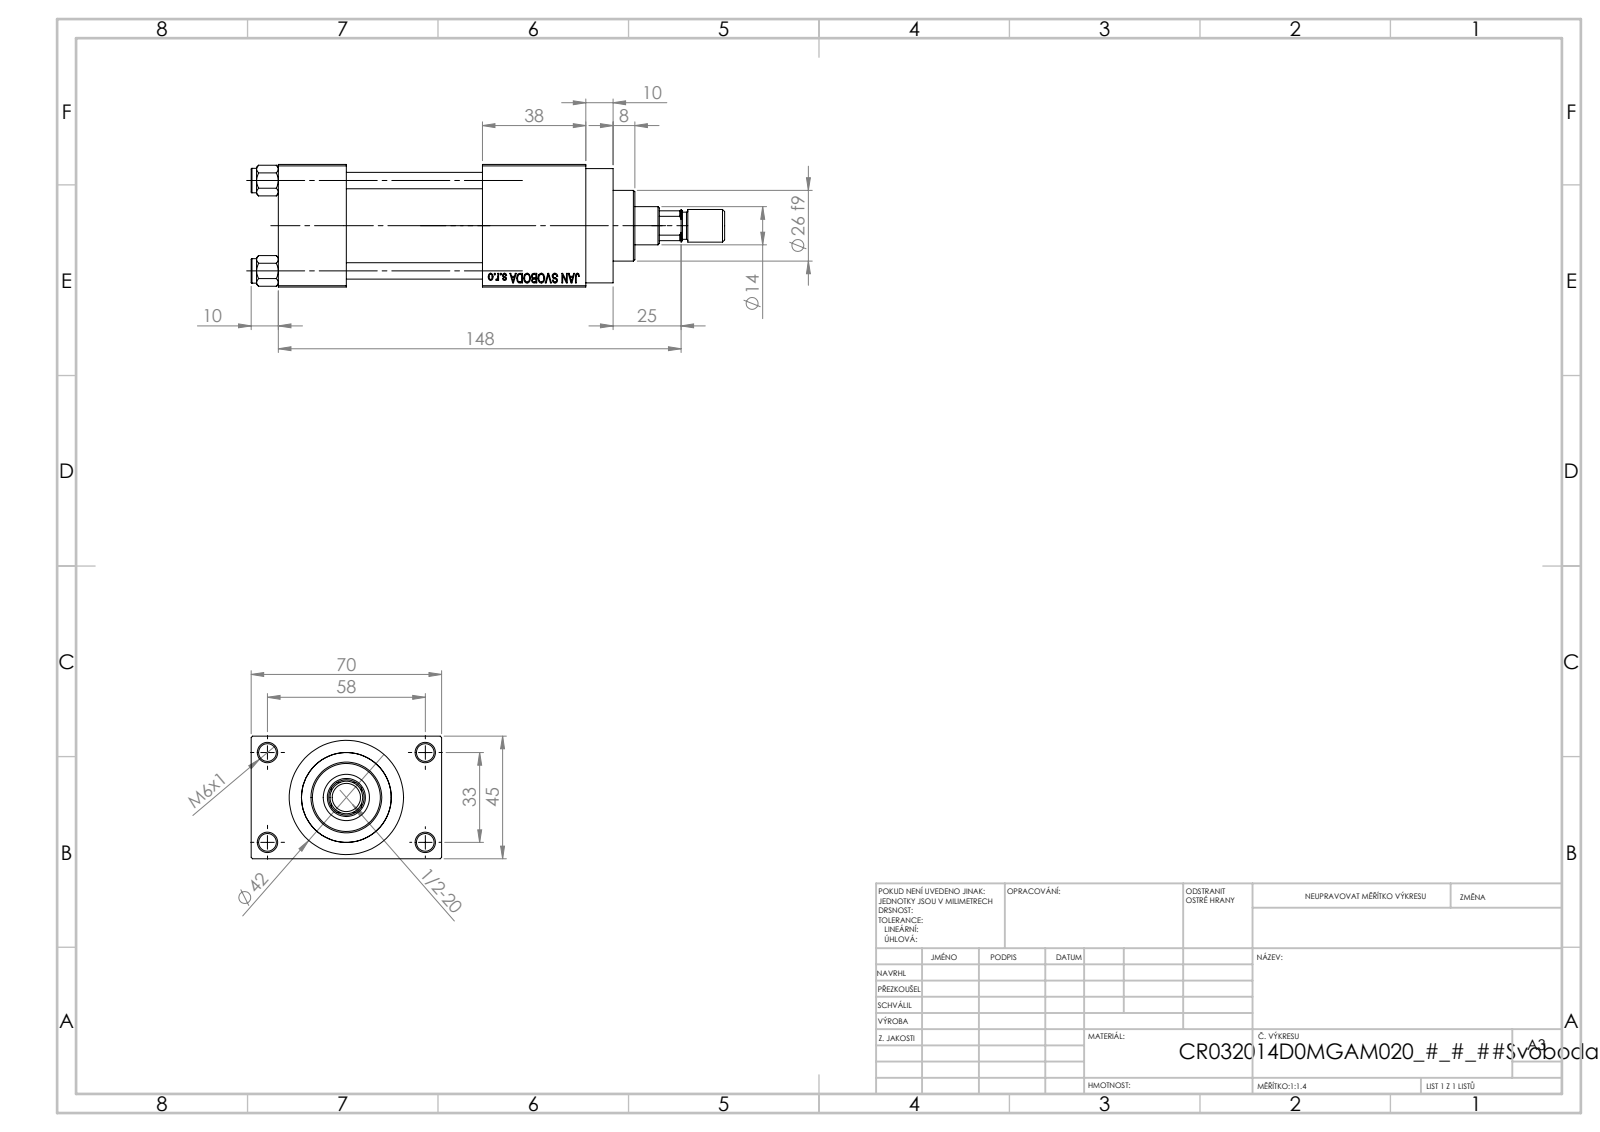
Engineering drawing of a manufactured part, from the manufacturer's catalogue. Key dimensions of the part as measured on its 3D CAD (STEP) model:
Part name (STEP PRODUCT): V215CR_D_TYCINKA; V215_VC_A; ROD_END_AH; V215CR_VCP_D (+2 more)
STEP written by: SolidWorks 2019 (CONFIG_CONTROL_DESIGN)
Units: millimetres
Bodies: 12 solids, 1117 faces (500 planar, 93 cylindrical, 524 other)
Overall size (bounding box): 174 × 70 × 45
Volume: 233 673 mm³ · Surface area: 75 722 mm²
Round holes (diameter × count): ⌀6.5 ×5, ⌀6 ×4, ⌀7 ×2, ⌀13.16 ×2, ⌀20 ×2, ⌀14 ×1, ⌀17 ×1, ⌀24 ×1, ⌀32 ×1, ⌀33 ×1
Round bosses / shafts (diameter × count): ⌀9 ×4, ⌀42 ×1, ⌀38 ×1, ⌀26 ×1, ⌀12 ×1, ⌀10 ×1
Partial cylindrical surfaces — rounded edges, fillets, slot ends (radius × count): R6.5 ×1
Main face-to-face distances: 45, 25, 12.5, 57.5, 50, 75, 88, 70, 38, 113
Hole centre spacings: 12.4, 23.48, 33.2, 33.37, 35.35, 45.6, 56.35, 33
